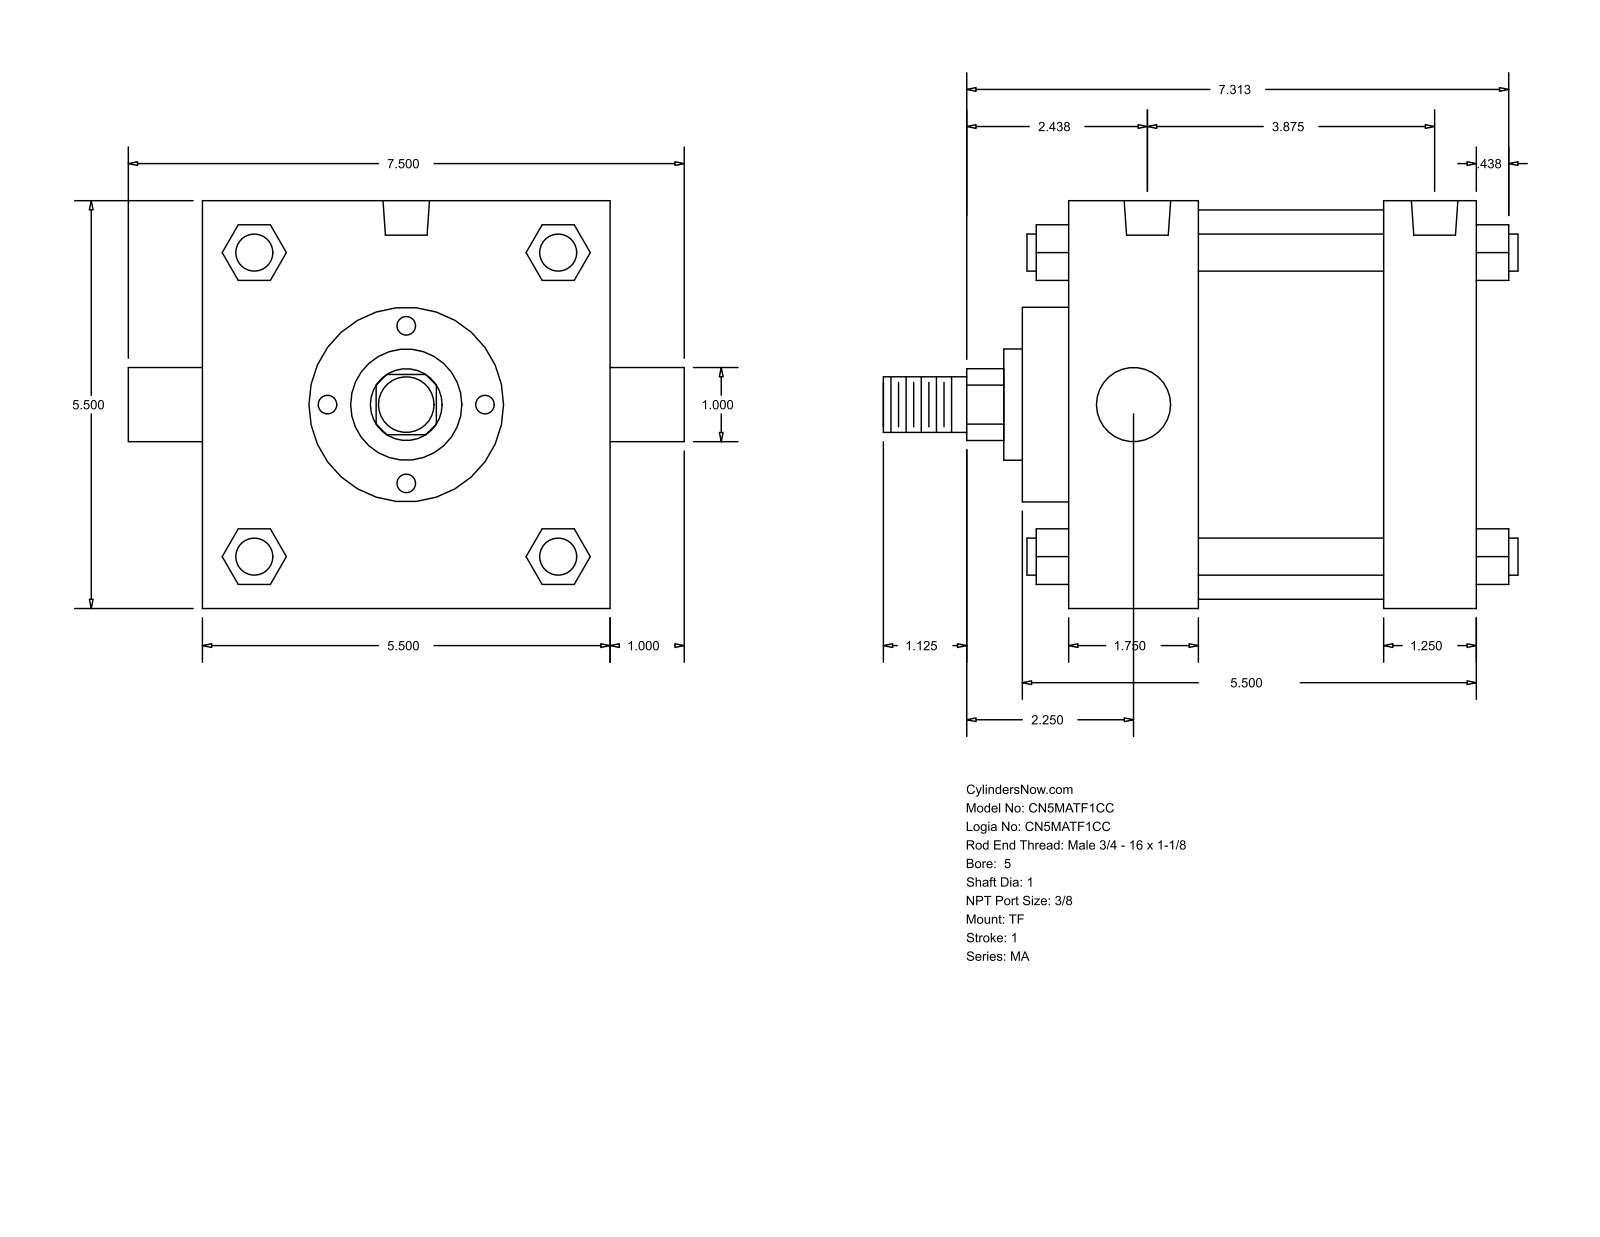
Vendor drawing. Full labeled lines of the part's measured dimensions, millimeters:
Part name (STEP PRODUCT): MA_TF__0500_1
STEP written by: GSSL Pune (CONFIG_CONTROL_DESIGN)
Units: millimetres
Bodies: 0 solids, 122 faces (93 planar, 29 cylindrical, 0 other)
Overall size (bounding box): 217.49 × 190.5 × 139.7
Round holes (diameter × count): ⌀11.11 ×3, ⌀15.93 ×2
Round bosses / shafts (diameter × count): ⌀12.7 ×4, ⌀25.4 ×2, ⌀133.35 ×1, ⌀66.67 ×1, ⌀38.1 ×1, ⌀19.05 ×1
Partial cylindrical surfaces — rounded edges, fillets, slot ends (radius × count): R12.29 ×1
Main face-to-face distances: 139.7, 107.96, 31.74, 44.46, 63.5, 95.24, 15.87, 60.33, 123.83, 155.57
Hole centre spacings: 4.76, 4.77, 88.9, 93.66, 93.67, 98.43
